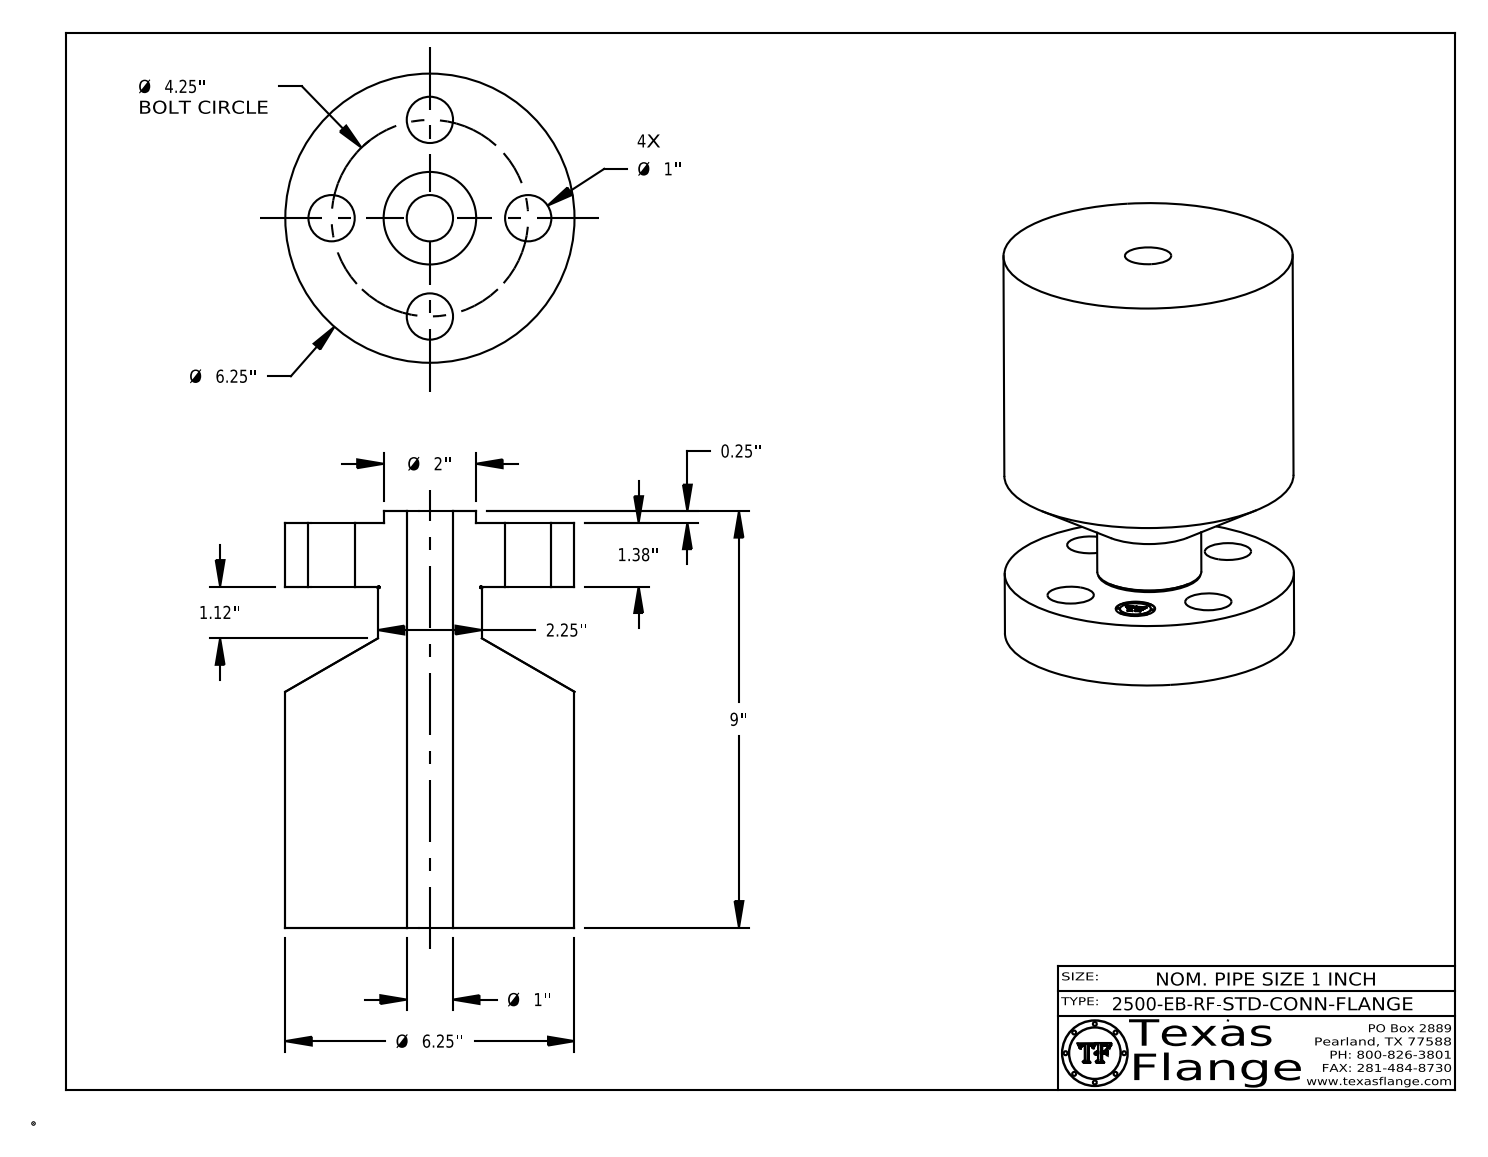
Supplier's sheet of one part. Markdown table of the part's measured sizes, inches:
| quantity | value |
| --- | --- |
| part name | 1-2500-EB-RF-STD-CONN-FLANGE |
| STEP written by | CATIA V5 STEP AP214 (AUTOMOTIVE_DESIGN) |
| units | inches |
| bodies | 1 solid, 413 faces (369 planar, 38 cylindrical, 6 other) |
| overall size | 9 × 6.25 × 6.25 |
| volume | 210.1 in³ |
| surface area | 293.6 in² |
| round holes (diameter × count) | 1 × 5, 0.85 × 1 |
| round bosses / shafts (diameter × count) | 0.051 × 8, 6.25 × 1, 2.25 × 1, 2 × 1, 0.67 × 1 |
| main face-to-face distances | 8.75, 1.38, 7.37, 0.25, 1.63, 9, 1.625, 1.375, 7.375, 0.254 |
| hole center spacings | 2.125, 3.006, 1.626, 3.927, 4.25 |
